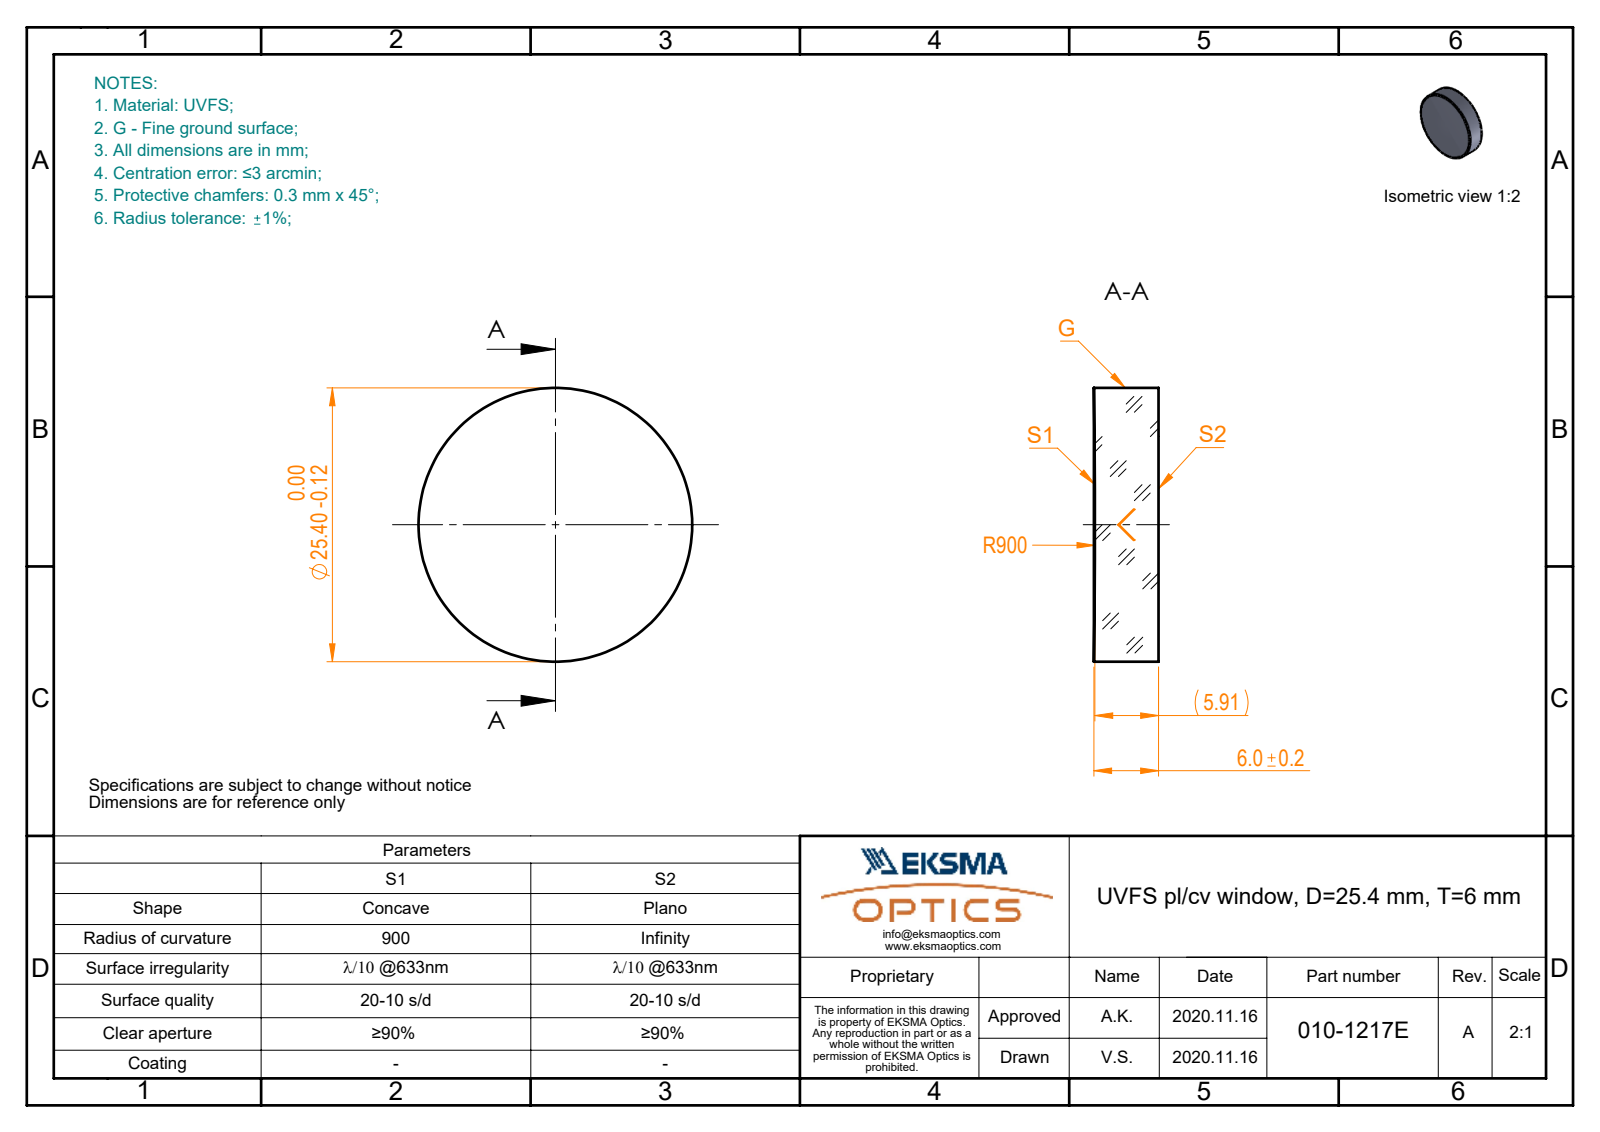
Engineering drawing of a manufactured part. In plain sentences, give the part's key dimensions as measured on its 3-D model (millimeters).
The part is named "010-1217E_UVFS_PCV_window". Its 3-D file was written by "SolidWorks 2019 (CONFIG_CONTROL_DESIGN)". It is 1 solid with 5 faces: 1 planar, 2 cylindrical and 2 other. Overall it measures 25.4 by 25.4 by 6 millimeters. Its volume is 3 018 cubic millimeters and its surface area 1 492 square millimeters. Round bosses or shafts: 1 of diameter 25.4.
